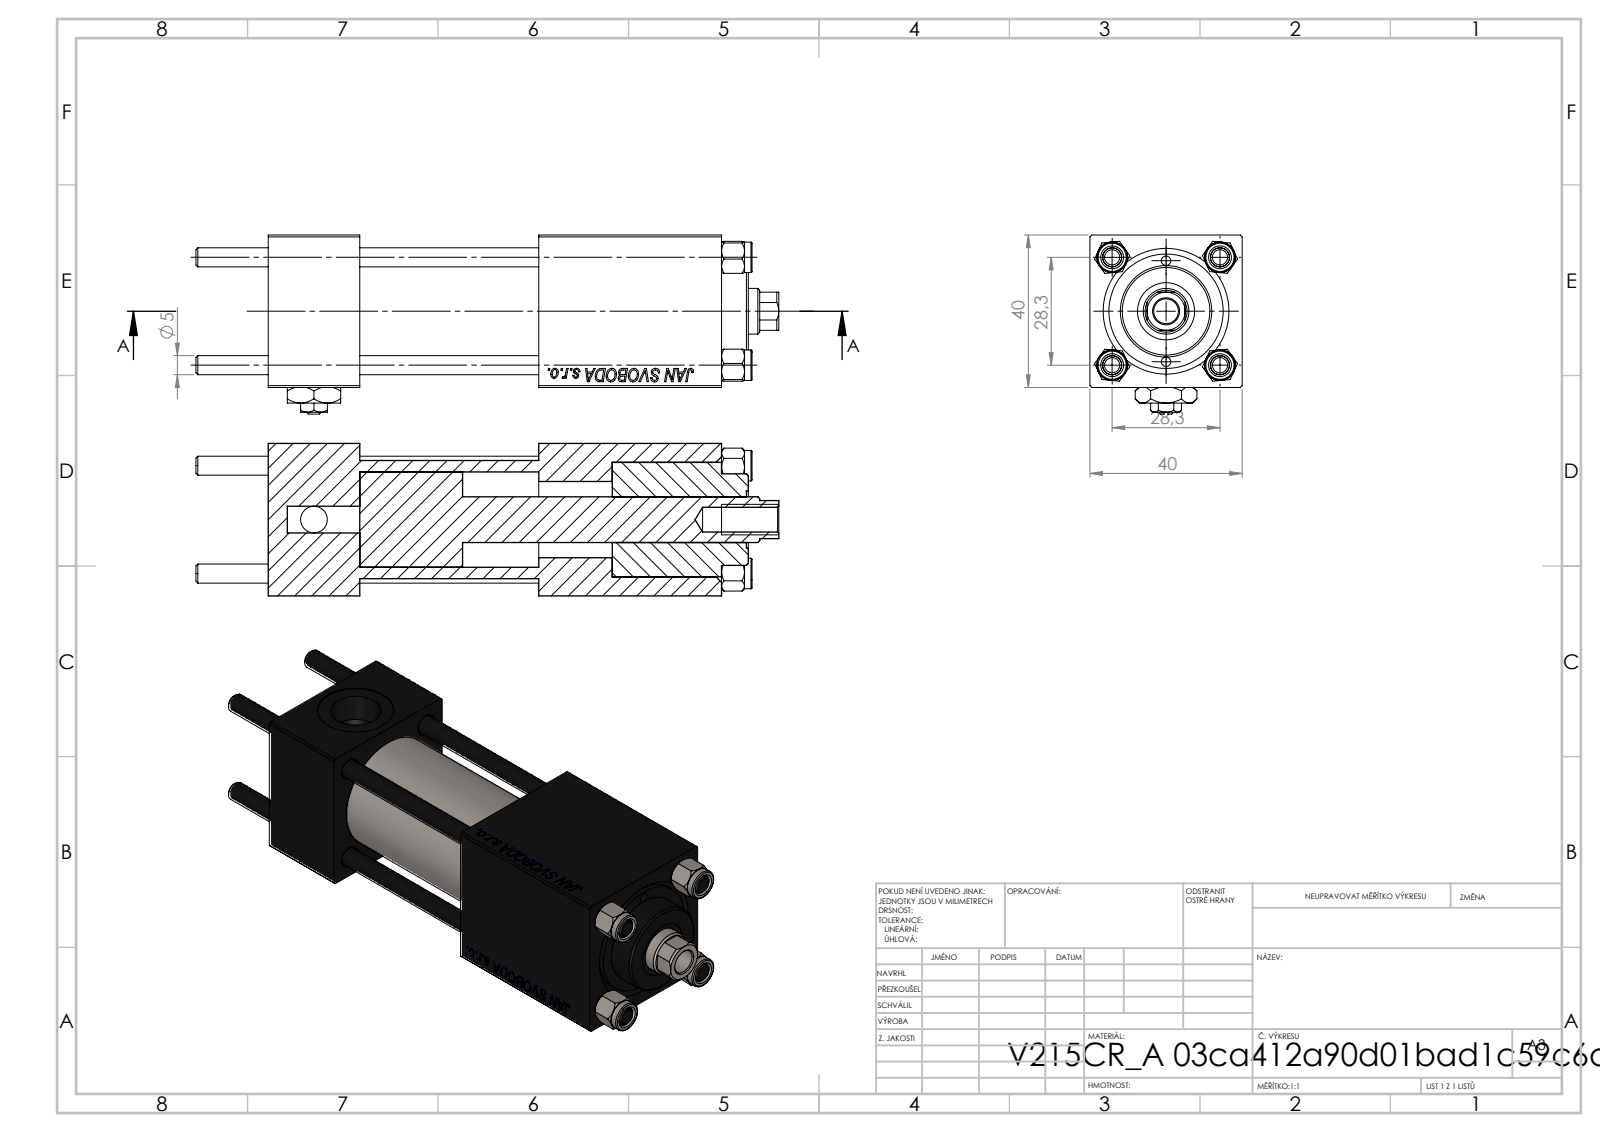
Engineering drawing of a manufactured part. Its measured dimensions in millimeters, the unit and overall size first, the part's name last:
Units: millimetres
Overall size (bounding box): 153 × 47 × 40
Round holes (diameter × count): ⌀5 ×4, ⌀20 ×3, ⌀2.5 ×2, ⌀7 ×2, ⌀13.16 ×2, ⌀6.5 ×1, ⌀12 ×1, ⌀15 ×1, ⌀25 ×1, ⌀30 ×1
Round bosses / shafts (diameter × count): ⌀8 ×4, ⌀31 ×1, ⌀24 ×1
Partial cylindrical surfaces — rounded edges, fillets, slot ends (radius × count): R5.5 ×1
Main face-to-face distances: 40, 24, 95, 90.3, 66.3, 119, 28.7, 47, 71, 19.3
Hole centre spacings: 14.18, 20.01, 28.3, 30.84, 13.25, 40.02, 26.5, 72
Volume: 144 022 mm³ · Surface area: 59 974 mm²
Bodies: 12 solids, 1190 faces (542 planar, 90 cylindrical, 558 other)
Part name (STEP PRODUCT): V215_VC_A; NUT_M5; V215CR_BODY_A; V215CR_VCP (+2 more)
STEP written by: SolidWorks 2019 (CONFIG_CONTROL_DESIGN)
